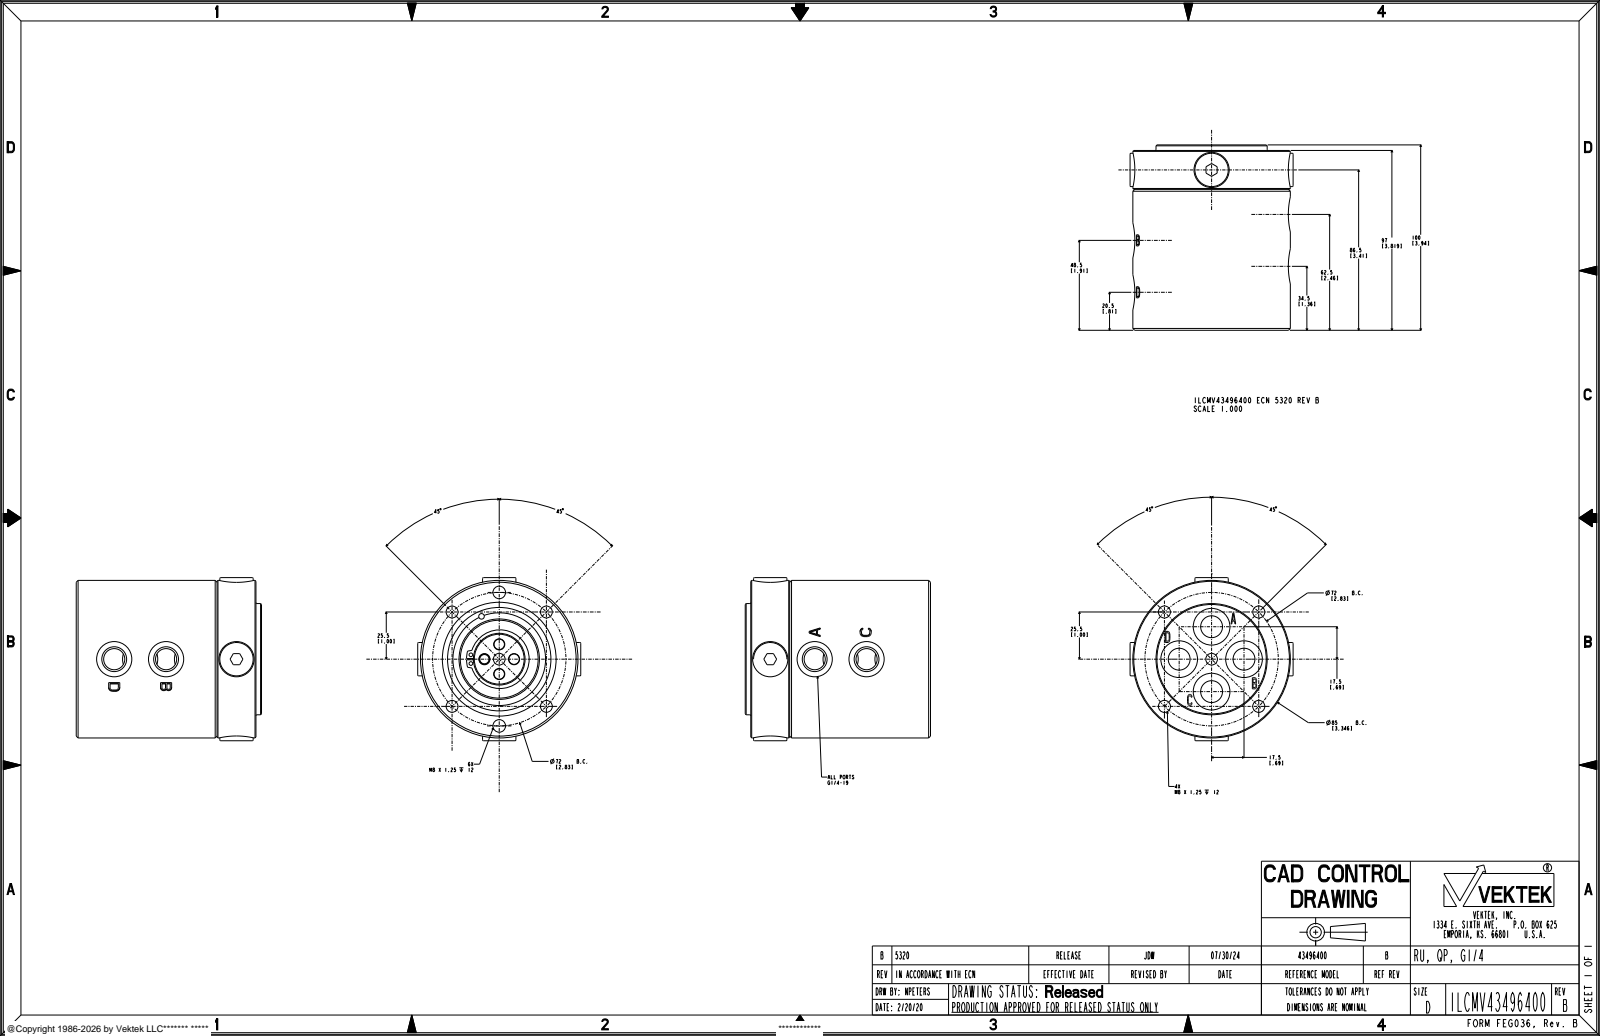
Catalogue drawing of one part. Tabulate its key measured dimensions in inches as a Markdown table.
| quantity | value |
| --- | --- |
| part name | ILCMV43496400 |
| STEP written by | CREO PARAMETRIC BY PTC INC, 2021164 (AUTOMOTIVE_DESIGN) |
| units | inches |
| bodies | 0 solids, 408 faces (236 planar, 118 cylindrical, 54 other) |
| overall size | 3.937 × 3.465 × 3.465 |
| round holes (diameter × count) | 0.465 × 6, 0.748 × 6, 0.236 × 4, 0.252 × 4, 0.256 × 4, 0.449 × 4, 0.78 × 4, 0.079 × 2, 0.268 × 2, 0.118 × 1, 0.197 × 1, 1.654 × 1 |
| round bosses / shafts (diameter × count) | 0.709 × 2, 3.346 × 1, 2.362 × 1, 2.197 × 1, 1.245 × 1, 1.098 × 1 |
| partial cylindrical surfaces (radius × count) | 0.695 × 1 |
| main face-to-face distances | 3.819, 2.992, 0.827, 0.118, 0.059, 3.937, 0.945, 3.878, 0.886, 3.807 |
| hole center spacings | 0.757, 1.05, 1.215, 1.656, 1.966, 0.315, 0.374, 0.445 |
